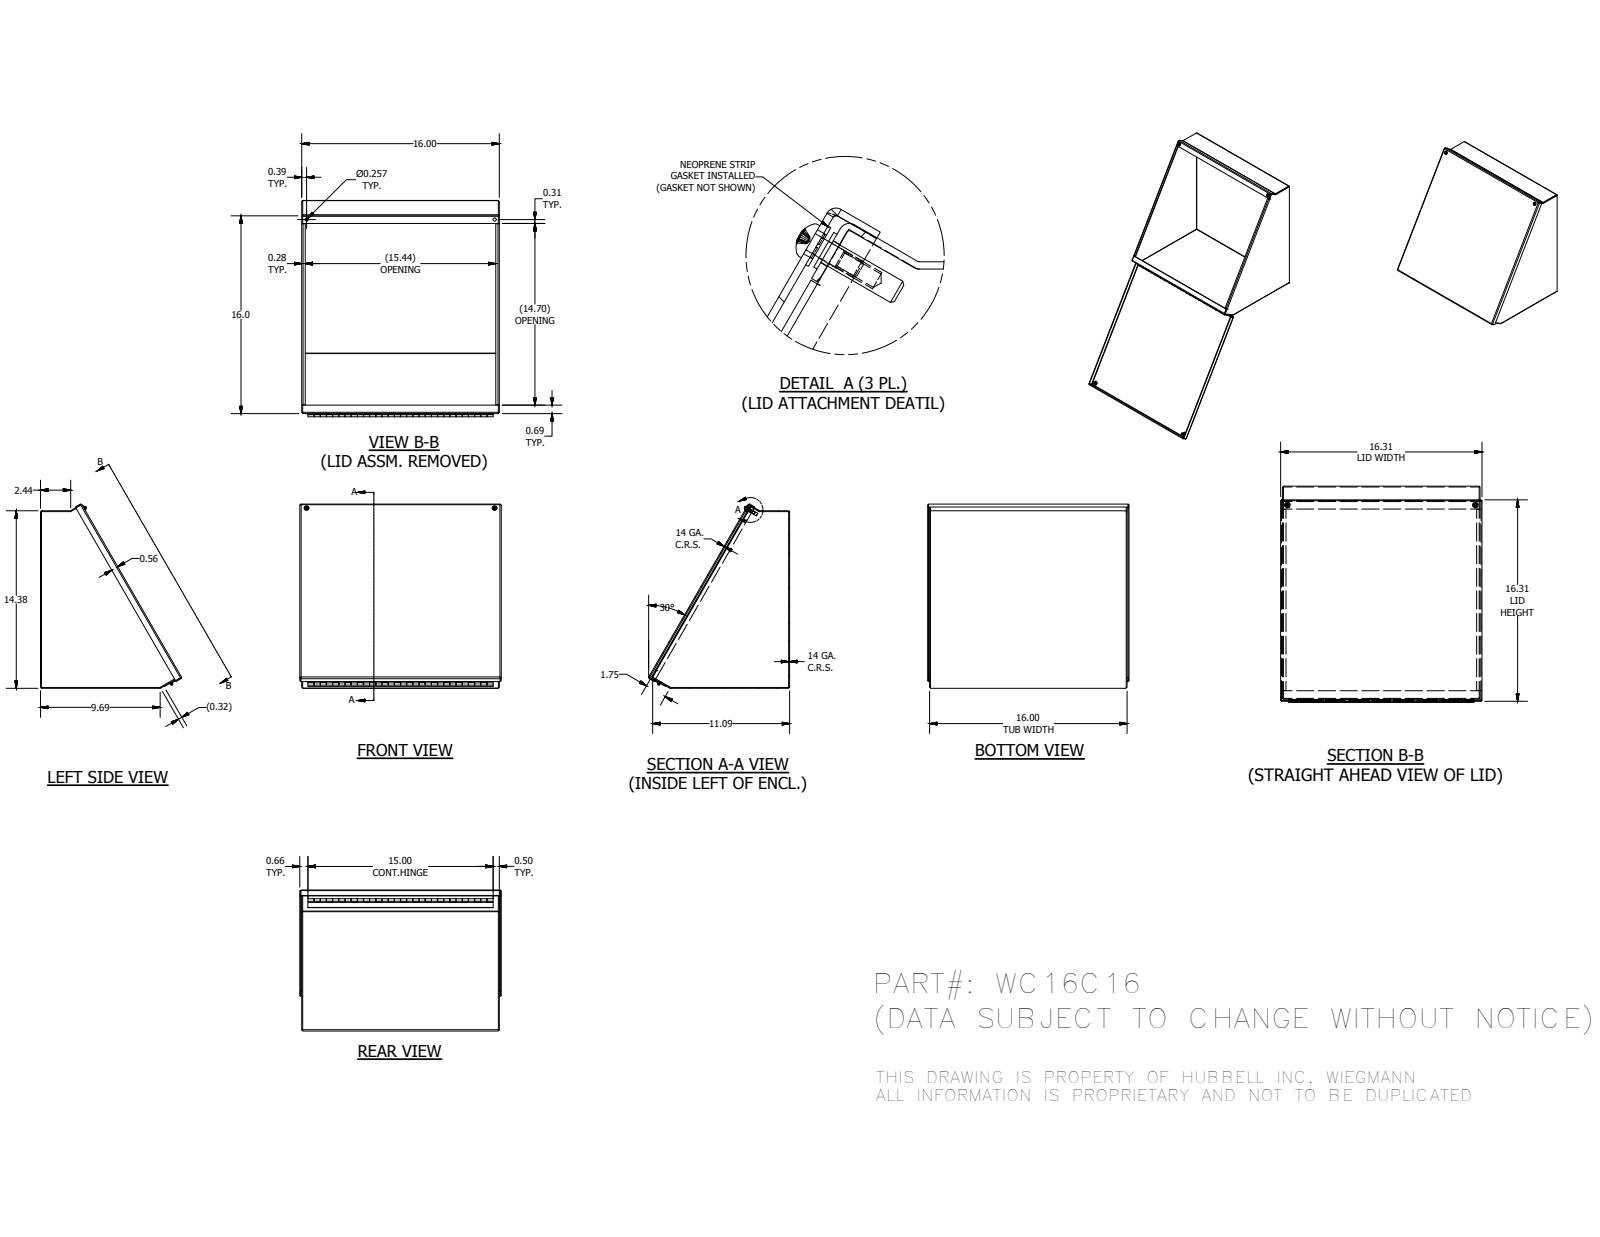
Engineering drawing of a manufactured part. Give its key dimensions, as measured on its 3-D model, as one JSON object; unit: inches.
{"part_name": "WC16C16BTB; WC16C16LID; WC16CLS; WC16CRS (+7 more)", "step_written_by": "Autodesk Inventor 2014 (AUTOMOTIVE_DESIGN)", "units": "inches", "bodies": {"solids": 13, "faces": 447, "planar": 282, "cylindrical": 113, "other": 52}, "overall_size": [16.313, 14.918, 11.42], "volume_in3": 74.51, "surface_area_in2": 2062, "round_holes": [[0.156, 2], [0.196, 2], [0.257, 2], [0.278, 2], [0.281, 2], [0.117, 1]], "round_bosses_or_shafts": [[0.453, 2], [0.406, 2], [0.373, 2], [0.248, 2], [0.19, 2], [0.2, 1], [0.1, 1]], "partial_cylinders_radius": [[0.031, 12], [0.105, 12], [0.089, 2]], "face_to_face_distances": [0.074, 15.926, 15.852, 16, 14.301, 14.227, 0.074, 14.375, 14.301, 0.156], "hole_center_spacings": [15.226]}
